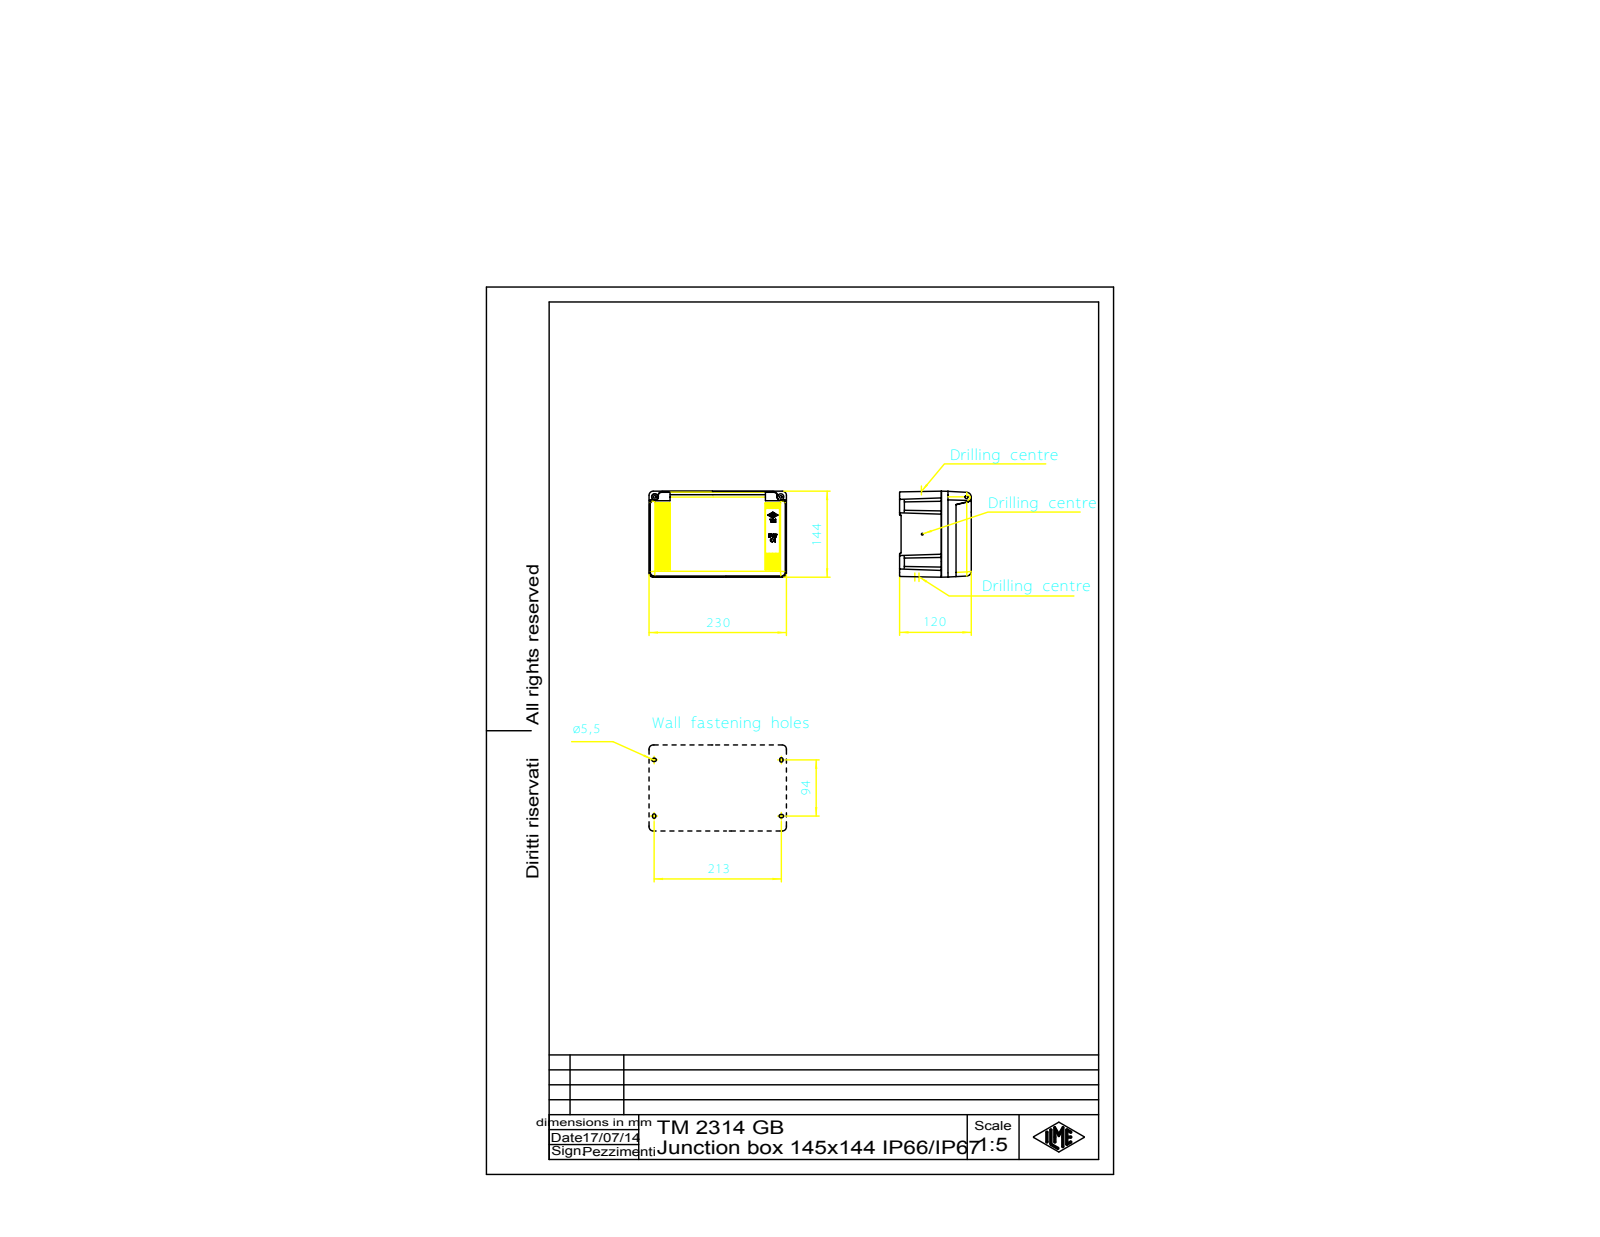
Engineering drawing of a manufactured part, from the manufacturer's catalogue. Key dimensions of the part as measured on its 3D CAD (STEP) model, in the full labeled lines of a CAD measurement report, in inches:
Part name (STEP PRODUCT): SPORTELLO_2314; SCATOLA_2314; CALOTTA_2314; TM_2314_GB
STEP written by: Creo Elements/Direct Modeling 20.5B 27-May-2023 (C) Parametric Technology GmbH (AUTOMOTIVE_DESIGN)
Units: inches
Bodies: 3 solids, 1382 faces (950 planar, 297 cylindrical, 135 other)
Overall size (bounding box): 9.055 × 5.669 × 4.74
Volume: 79.94 in³ · Surface area: 579.5 in²
Round holes (diameter × count): ⌀0.205 ×6, ⌀0.197 ×1
Round bosses / shafts (diameter × count): ⌀0.335 ×6, ⌀0.197 ×6, ⌀0.264 ×2, ⌀0.157 ×2
Partial cylindrical surfaces — rounded edges, fillets, slot ends (radius × count): R0.008 ×124, R0.138 ×16, R0.118 ×12, R0.276 ×12, R0.01 ×11, R0.106 ×8, R0.315 ×8, R0.374 ×8
Main face-to-face distances: 0.197, 4.429, 2.657, 1.772, 3.622, 3.425, 4.626, 1.004, 0.211, 0.768
Hole centre spacings: 1.839, 4.851, 4.921, 6.529, 7.923, 8.307, 9.656, 4.724
